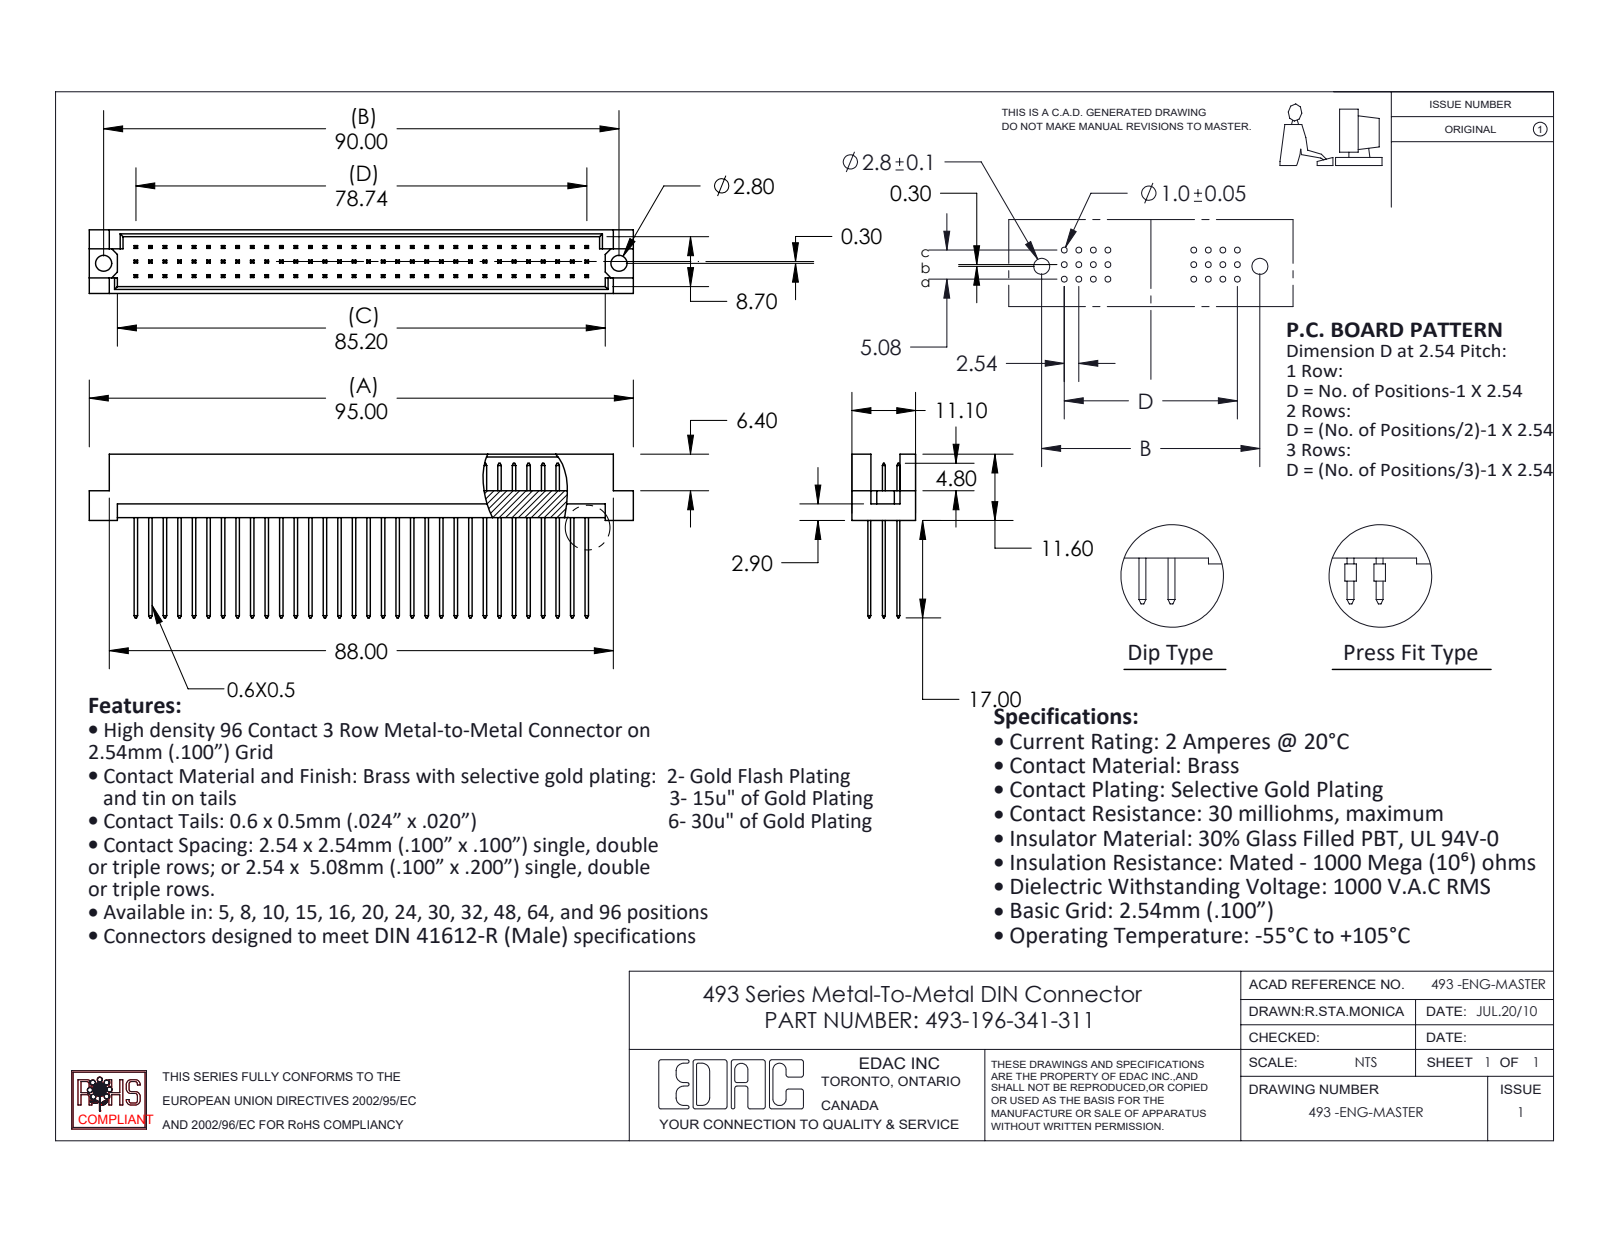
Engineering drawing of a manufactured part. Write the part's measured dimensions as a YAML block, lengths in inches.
part_name: "493-290_41; 493 Part_96; 493-196-341-311"
step_written_by: "SolidWorks 2020 (CONFIG_CONTROL_DESIGN)"
units: inches
bodies: {solids: 97, faces: 1780, planar: 1776, cylindrical: 4, other: 0}
overall_size: [3.74, 1.126, 0.437]
volume: 0.392
surface_area: 18.82
round_holes:
  - {diameter: 0.11, count: 2}
face_to_face_distances: [0.1, 0.2, 0.02, 0.047, 0.39, 0.109, 0.128, 0.209, 0.228, 0.309]
hole_center_spacings: [3.543]
